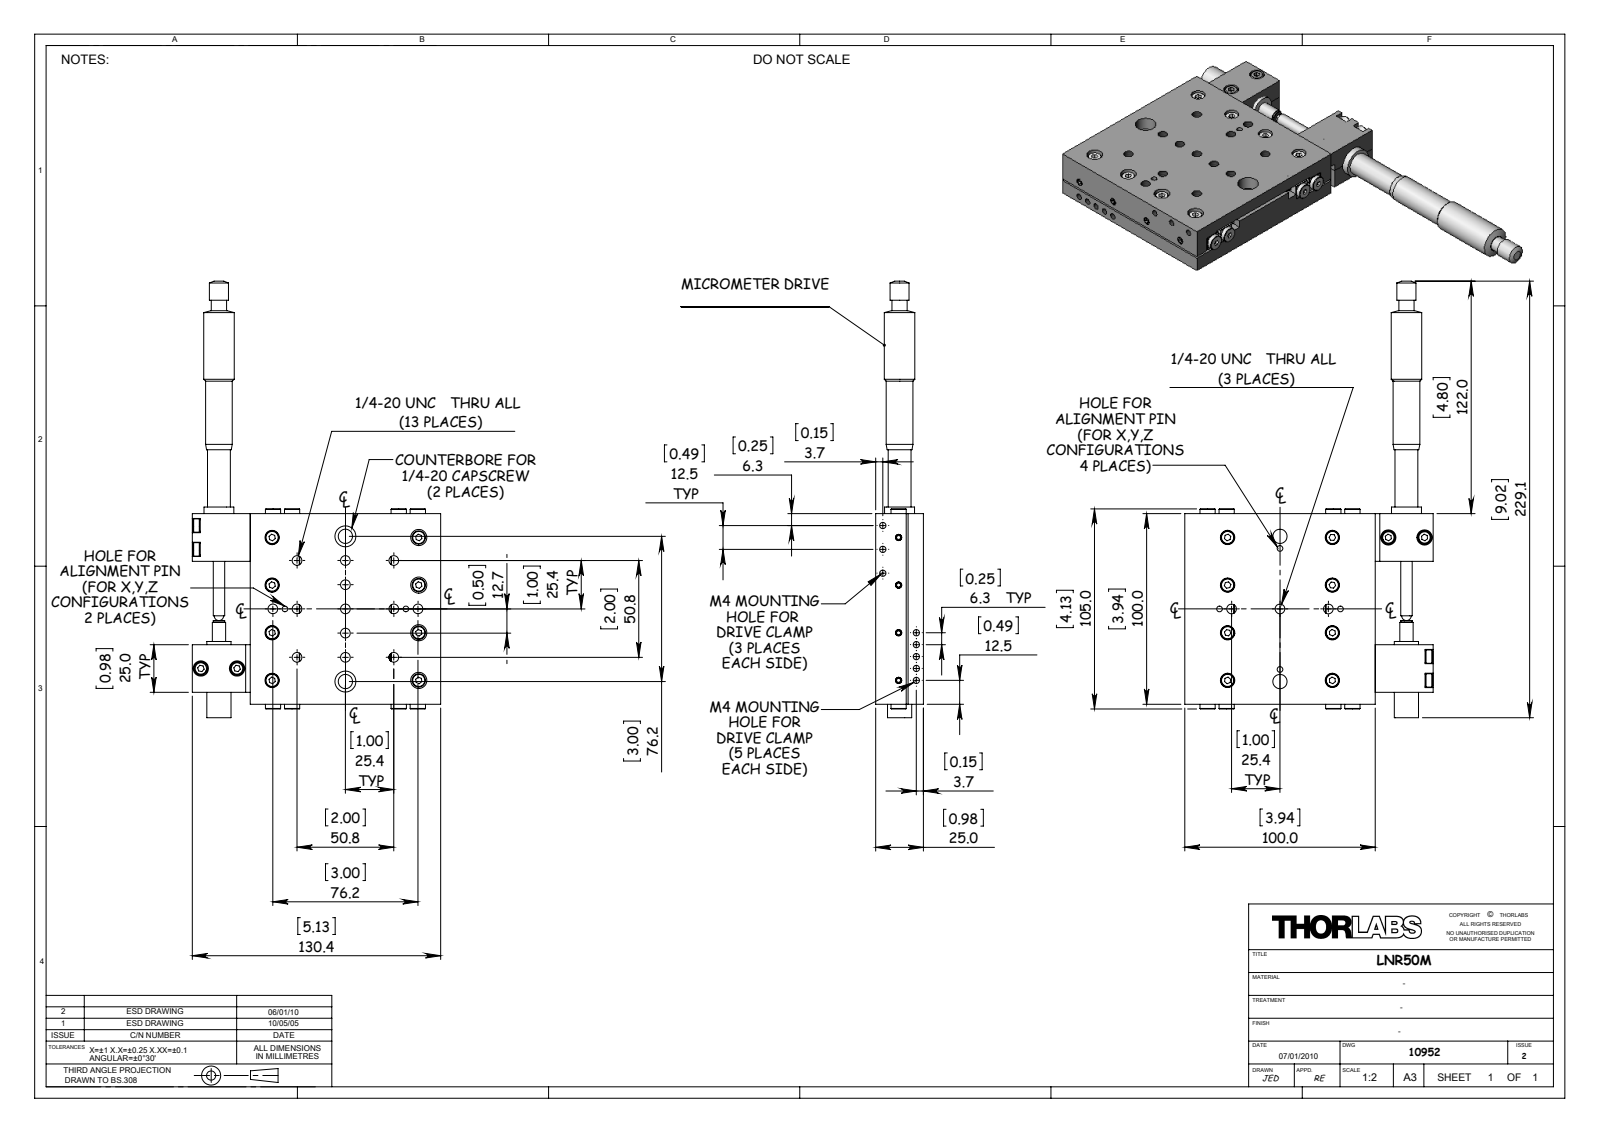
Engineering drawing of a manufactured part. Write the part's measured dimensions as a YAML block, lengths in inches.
part_name: "LNR50 With Micrometer"
step_written_by: "SolidWorks 2009 (AUTOMOTIVE_DESIGN)"
units: inches
bodies: {solids: 60, faces: 1581, planar: 706, cylindrical: 614, other: 261}
overall_size: [9.02, 5.134, 0.984]
volume: 16.15
surface_area: 189.7
round_holes:
  - {diameter: 0.13, count: 32}
  - {diameter: 0.079, count: 16}
  - {diameter: 0.236, count: 16}
  - {diameter: 0.295, count: 14}
  - {diameter: 0.201, count: 13}
  - {diameter: 0.177, count: 12}
  - {diameter: 0.169, count: 8}
  - {diameter: 0.157, count: 5}
  - {diameter: 0.098, count: 4}
  - {diameter: 0.119, count: 4}
  - {diameter: 0.217, count: 4}
  - {diameter: 0.315, count: 4}
round_bosses_or_shafts:
  - {diameter: 0.118, count: 38}
  - {diameter: 0.157, count: 26}
  - {diameter: 0.276, count: 25}
  - {diameter: 0.315, count: 5}
  - {diameter: 0.069, count: 4}
  - {diameter: 0.63, count: 1}
  - {diameter: 0.618, count: 1}
  - {diameter: 0.551, count: 1}
partial_cylinders:
  - {radius: 0.148, count: 4}
  - {radius: 0.236, count: 2}
  - {radius: 0.276, count: 2}
face_to_face_distances: [0.315, 0.354, 0.039, 0.276, 0.984, 0.63, 0.709, 0.669, 0.157, 3.937]
hole_center_spacings: [0.984, 0.246, 0.492, 3.002, 0.738, 1.068, 1.969, 2.379]
